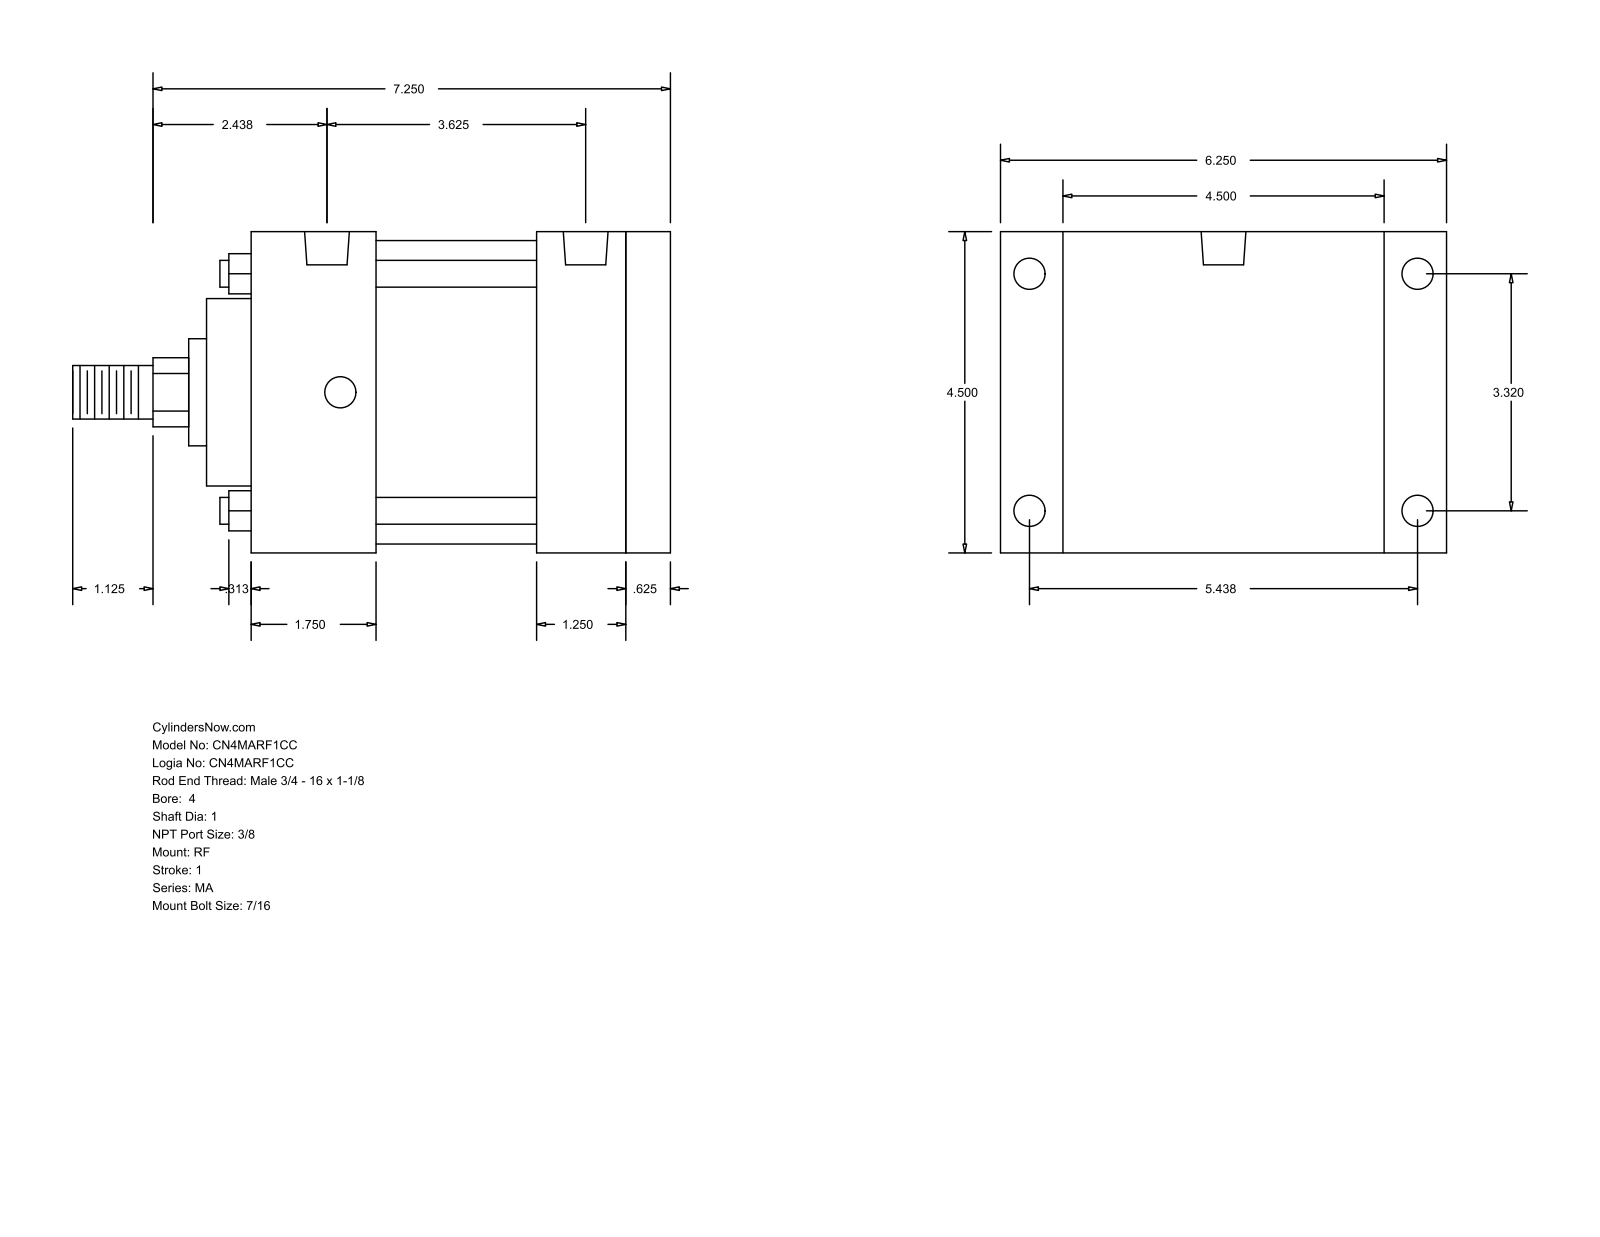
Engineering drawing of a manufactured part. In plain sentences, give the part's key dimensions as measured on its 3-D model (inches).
The part is named "MA_RF__0400_1". Its 3-D file was written by "GSSL Pune (CONFIG_CONTROL_DESIGN)". It is 0 solids with 94 faces: 65 planar, 29 cylindrical and 0 other. Overall it measures 8.375 by 6.25 by 4.5 inches. Round holes: 8 of diameter 0.437, 2 of diameter 0.627. Round bosses or shafts: 4 of diameter 0.375, 1 of diameter 4.25, 1 of diameter 2.625, 1 of diameter 1.5, 1 of diameter 1, 1 of diameter 0.75. Partial cylindrical surfaces (rounded edges, fillets, slot ends): 1 of radius 0.484. The main face-to-face distances are 4.5, 5.875, 0.625, 5.25, 1.875, 5.375, 0.875, 4, 1.25, 1.75. The hole center spacings are 3.25, 3.32, 5.438, 6.371, 0.187, 0.188, 3.437, 3.438.
